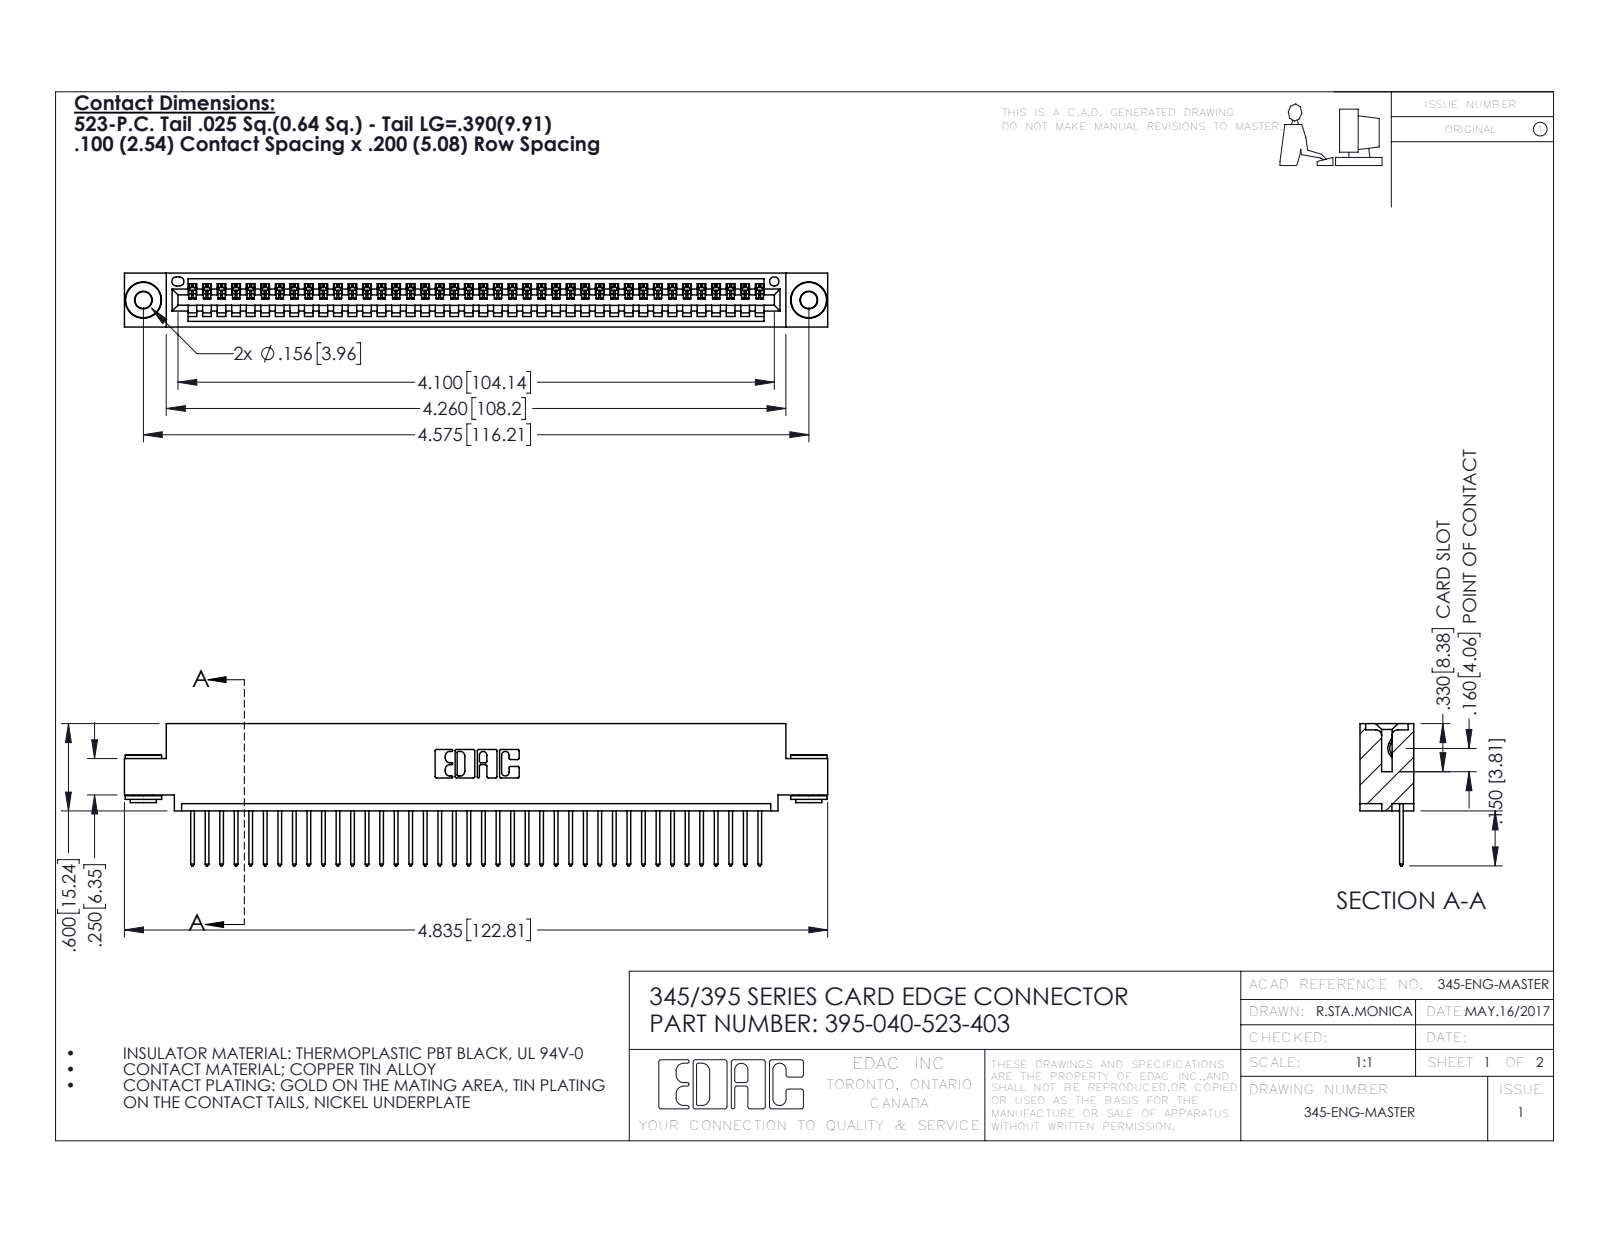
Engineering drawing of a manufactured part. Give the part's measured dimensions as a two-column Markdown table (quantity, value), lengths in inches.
| quantity | value |
| --- | --- |
| part name | 345 Part_0.110 Offset - 0.156 Dia-TH; 395-040-523-403; 345-292-001_345-293-123; 345-250-002_345-250-002-102 |
| STEP written by | SolidWorks 2016 (CONFIG_CONTROL_DESIGN) |
| units | inches |
| bodies | 43 solids, 2488 faces (1694 planar, 786 cylindrical, 8 other) |
| overall size | 4.835 × 0.977 × 0.37 |
| volume | 0.707 in³ |
| surface area | 24.33 in² |
| round holes (diameter × count) | 0.116 × 2, 0.156 × 2, 0.064 × 1 |
| round bosses / shafts (diameter × count) | 0.25 × 2, 0.18 × 2, 0.136 × 2 |
| partial cylindrical surfaces (radius × count) | 0.006 × 80, 0.01 × 80, 0.01 × 22, 0.007 × 6, 0.031 × 6, 0.026 × 3, 0.031 × 2, 0.04 × 2 |
| main face-to-face distances | 0.072, 0.298, 0.37, 0.025, 0.2, 0.098, 0.272, 0.225, 0.149, 0.072 |
| hole center spacings | 0.27, 4.339, 4.575 |
